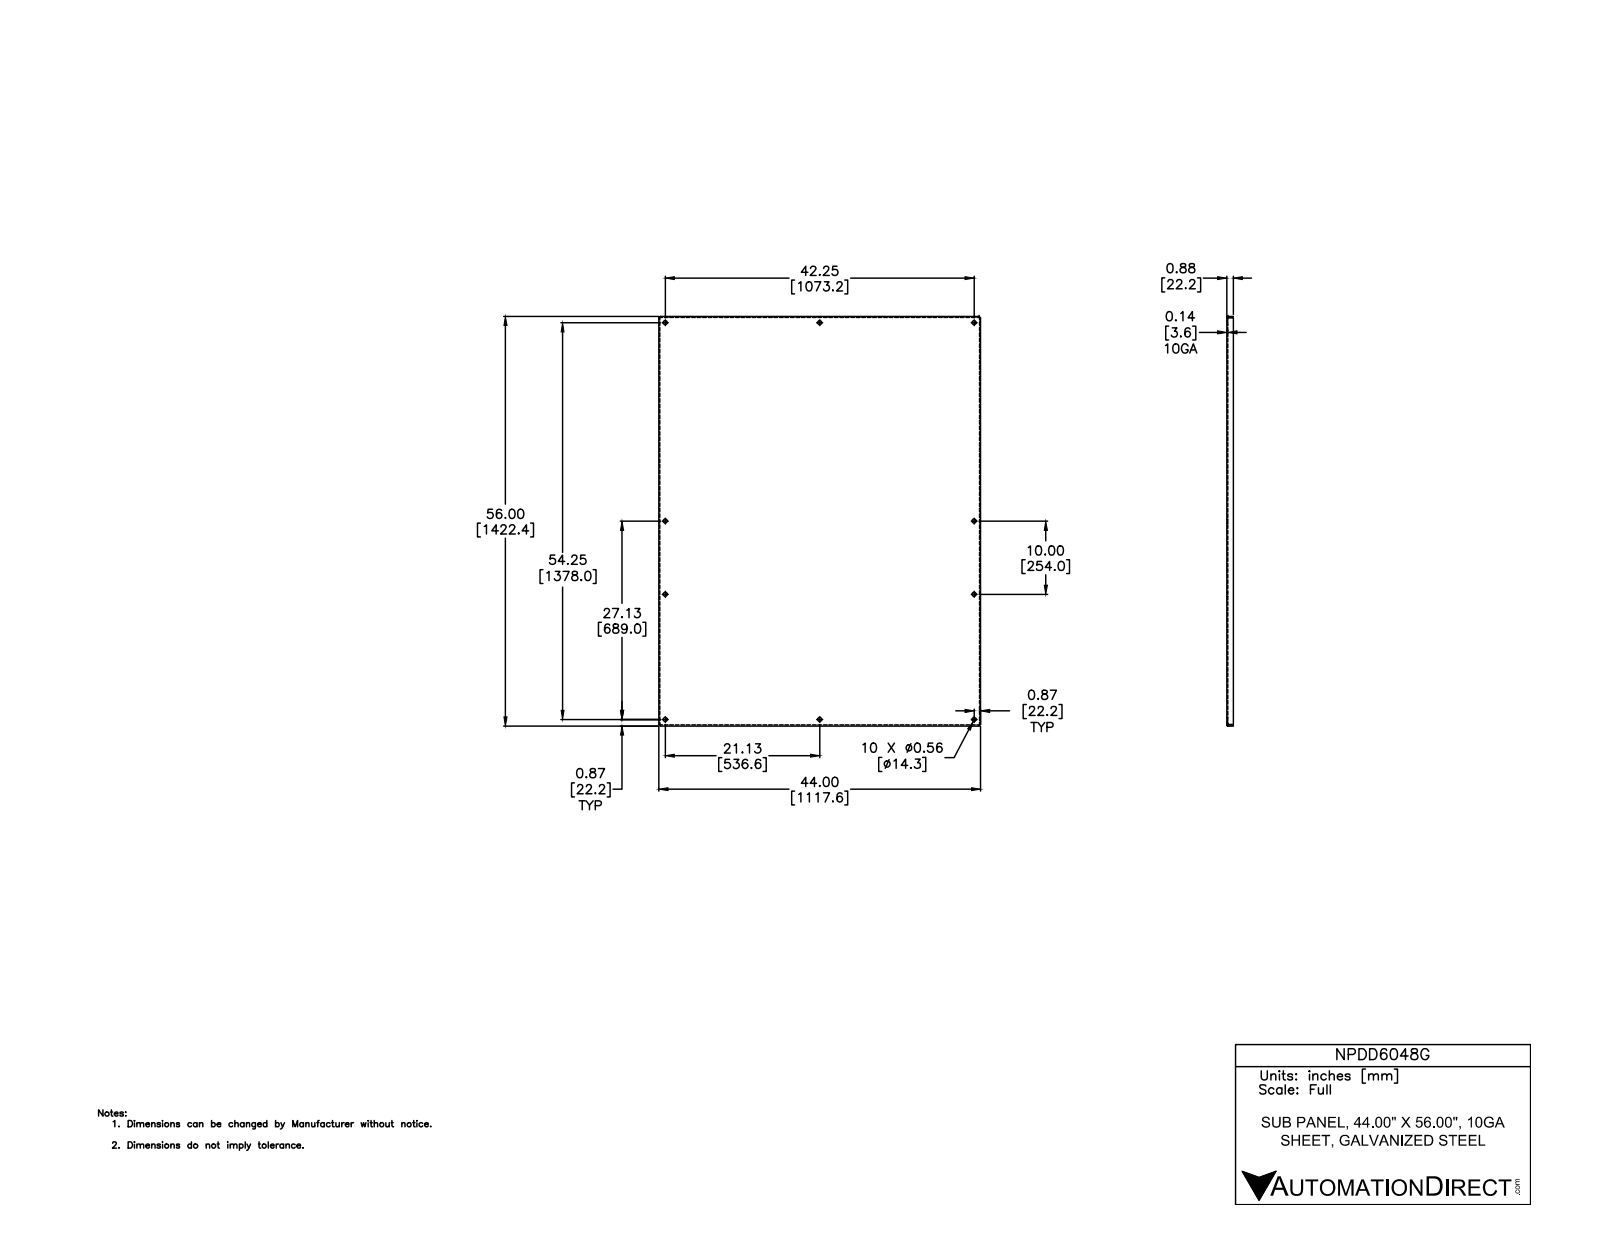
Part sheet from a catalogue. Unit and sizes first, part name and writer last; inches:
Units: inches
Overall size (bounding box): 56 × 44 × 0.875
Round holes (diameter × count): ⌀0.563 ×10
Partial cylindrical surfaces — rounded edges, fillets, slot ends (radius × count): R0.031 ×4, R0.156 ×4
Main face-to-face distances: 0.125, 43.875, 44, 43.75, 56, 55.875, 55.75, 55.875, 0.125, 0.75
Hole centre spacings: 21.125, 27.125, 58.219, 10, 27.194, 34.381, 34.381, 37.125
Volume: 325.3 in³ · Surface area: 5 232 in²
Bodies: 1 solid, 48 faces (22 planar, 18 cylindrical, 8 other)
Part name (STEP PRODUCT): NPDD4242G-NPDD7272G
STEP written by: Autodesk Inventor 2012 (AUTOMOTIVE_DESIGN)
